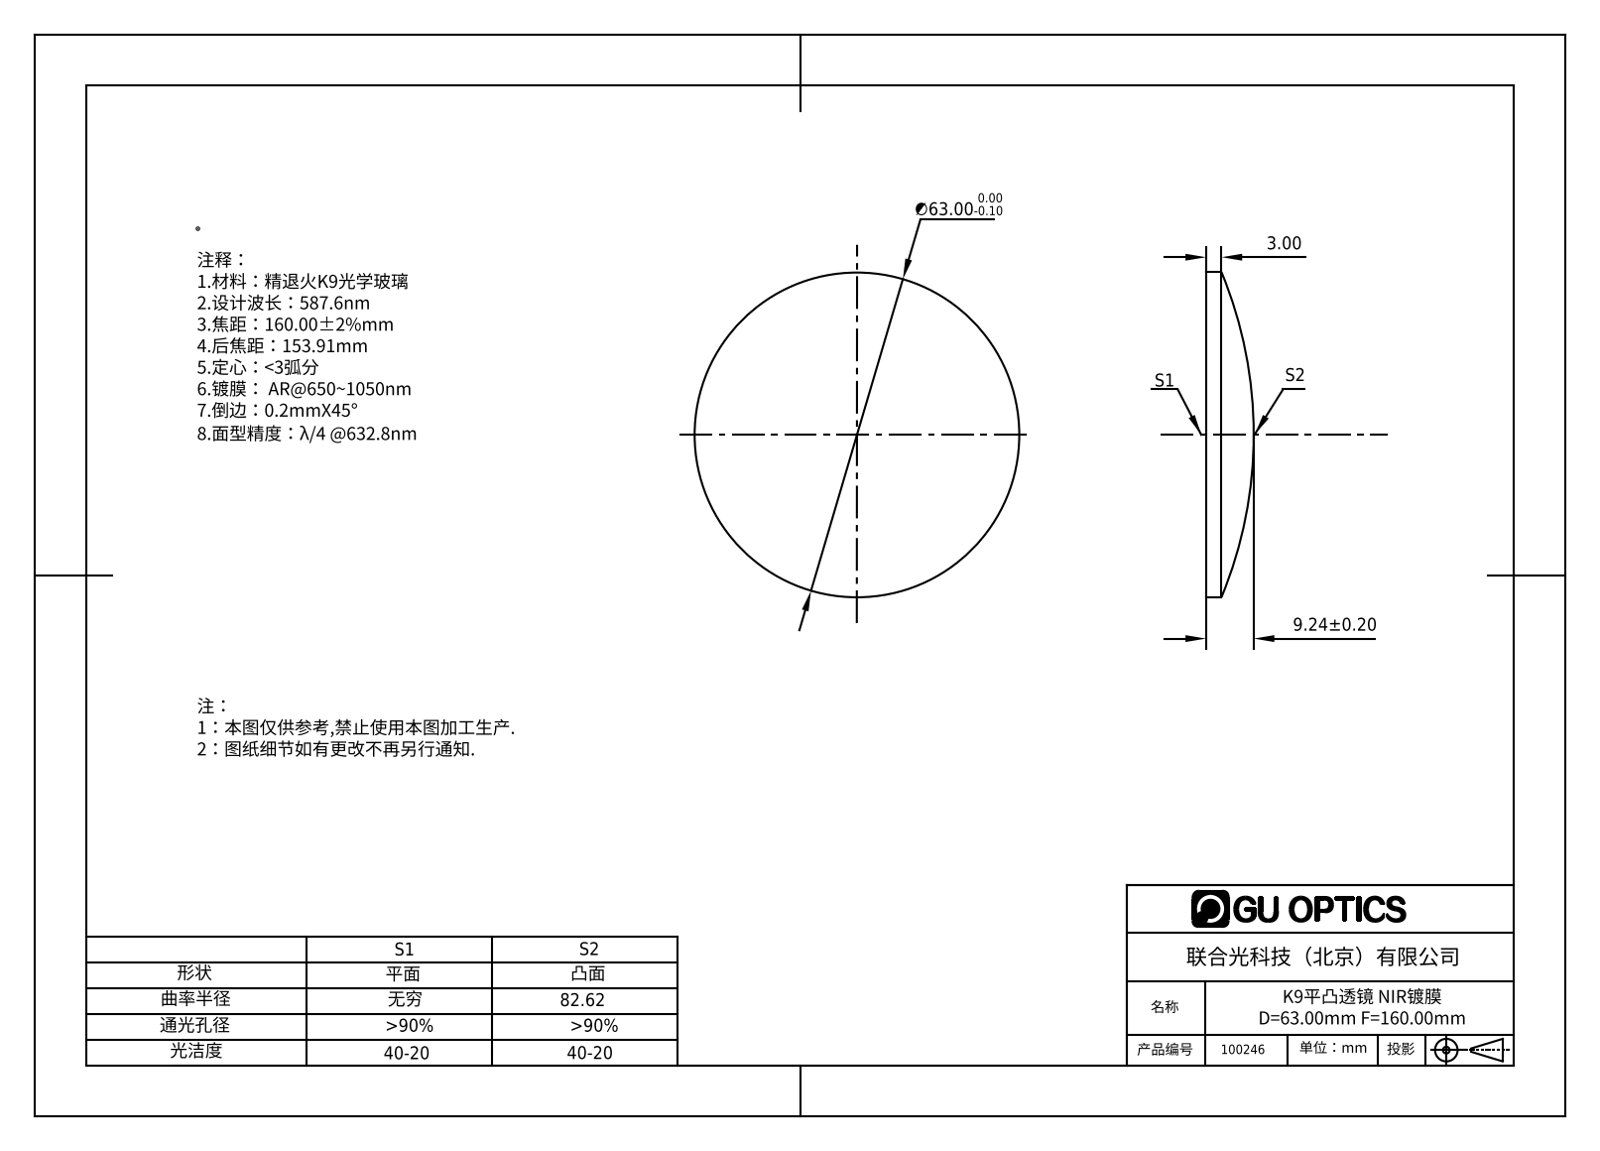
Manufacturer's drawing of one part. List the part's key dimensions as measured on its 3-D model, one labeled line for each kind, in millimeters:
Part name (STEP PRODUCT): 100246
STEP written by: SolidWorks 2016 (AUTOMOTIVE_DESIGN)
Units: millimetres
Bodies: 1 solid, 5 faces (1 planar, 2 cylindrical, 2 other)
Overall size (bounding box): 63 × 63 × 9.24
Volume: 19 205 mm³ · Surface area: 6 951 mm²
Round bosses / shafts (diameter × count): ⌀63 ×1
